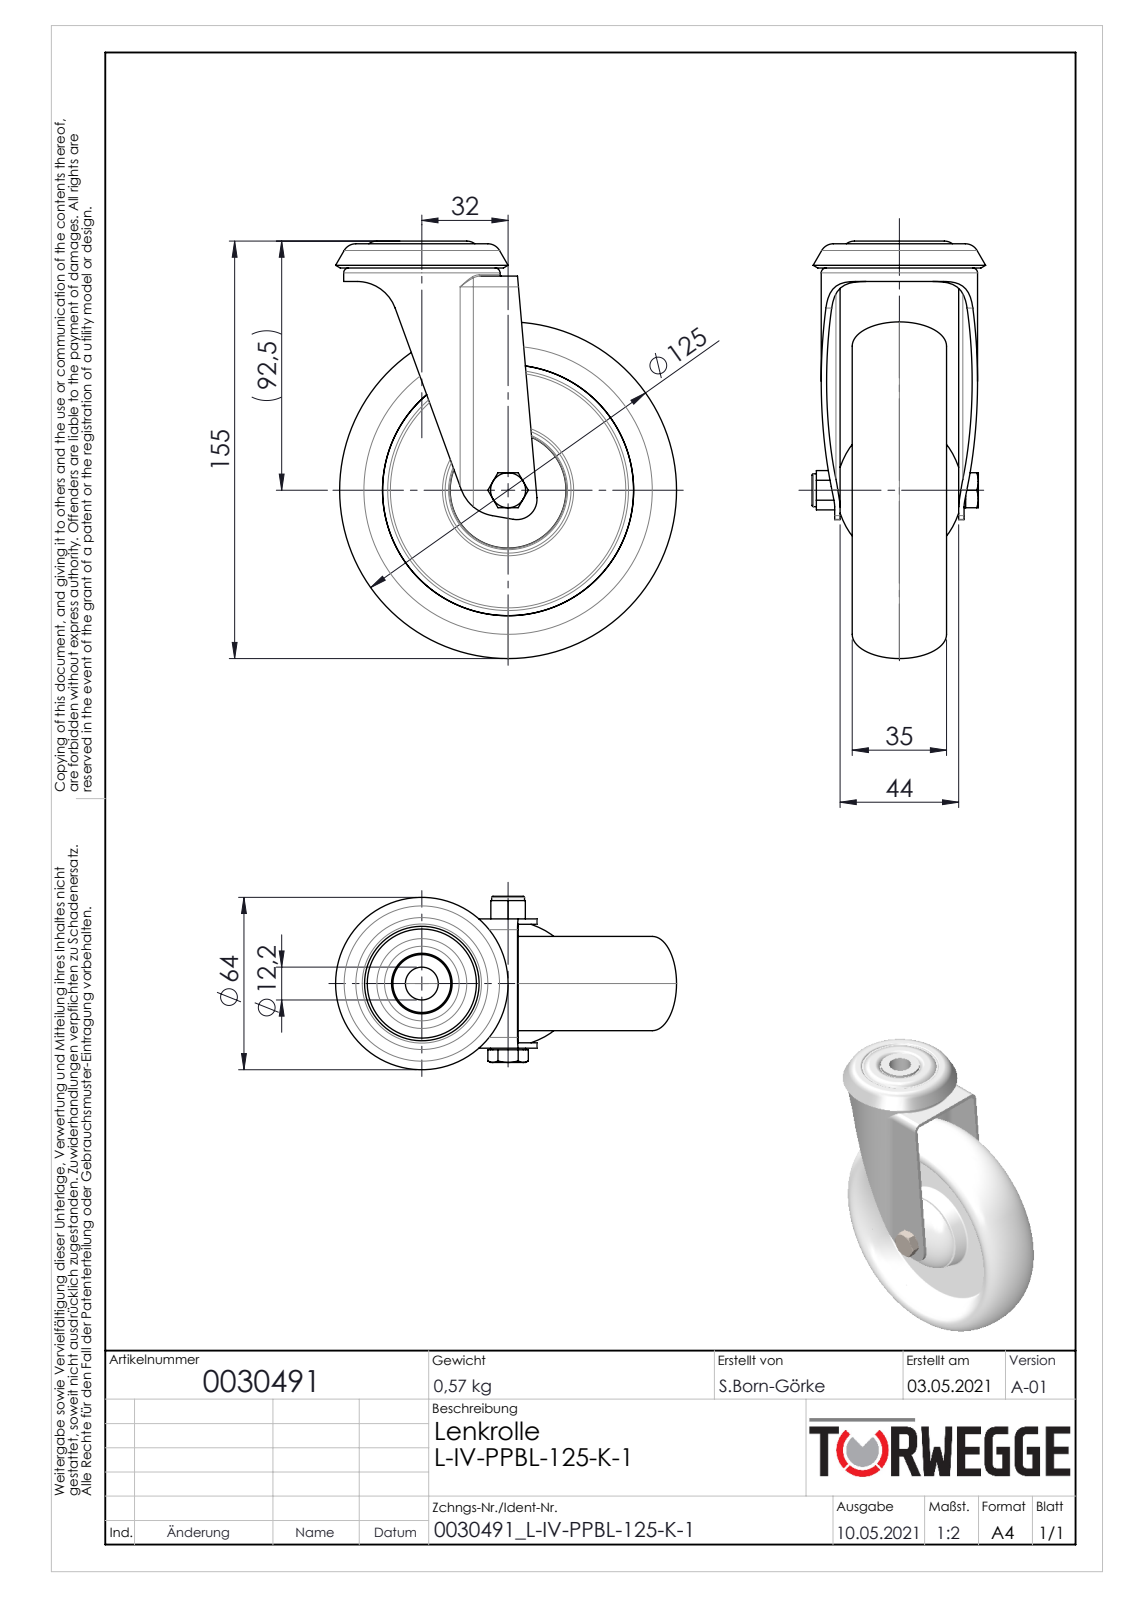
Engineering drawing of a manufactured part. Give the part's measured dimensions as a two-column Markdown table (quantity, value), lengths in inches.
| quantity | value |
| --- | --- |
| part name | 0030491 |
| STEP written by | SolidWorks 2020 (AUTOMOTIVE_DESIGN) |
| units | inches |
| bodies | 7 solids, 215 faces (59 planar, 52 cylindrical, 104 other) |
| overall size | 6.102 × 4.98 × 2.535 |
| volume | 17.09 in³ |
| surface area | 174.4 in² |
| round holes (diameter × count) | 0.262 × 1, 0.315 × 1, 0.323 × 1, 0.48 × 1, 1.299 × 1, 1.378 × 1, 2.126 × 1 |
| round bosses / shafts (diameter × count) | 2.283 × 1, 1.142 × 1, 0.846 × 1, 0.591 × 1, 0.512 × 1, 0.48 × 1 |
| partial cylindrical surfaces (radius × count) | 0.079 × 2, 0.157 × 2, 0.394 × 2, 0.472 × 2, 0.591 × 2, 0.295 × 1 |
| main face-to-face distances | 0.197, 0.079, 0.846, 0.768, 0.965, 1.043, 1.811, 0.522, 0.364, 0.482 |
